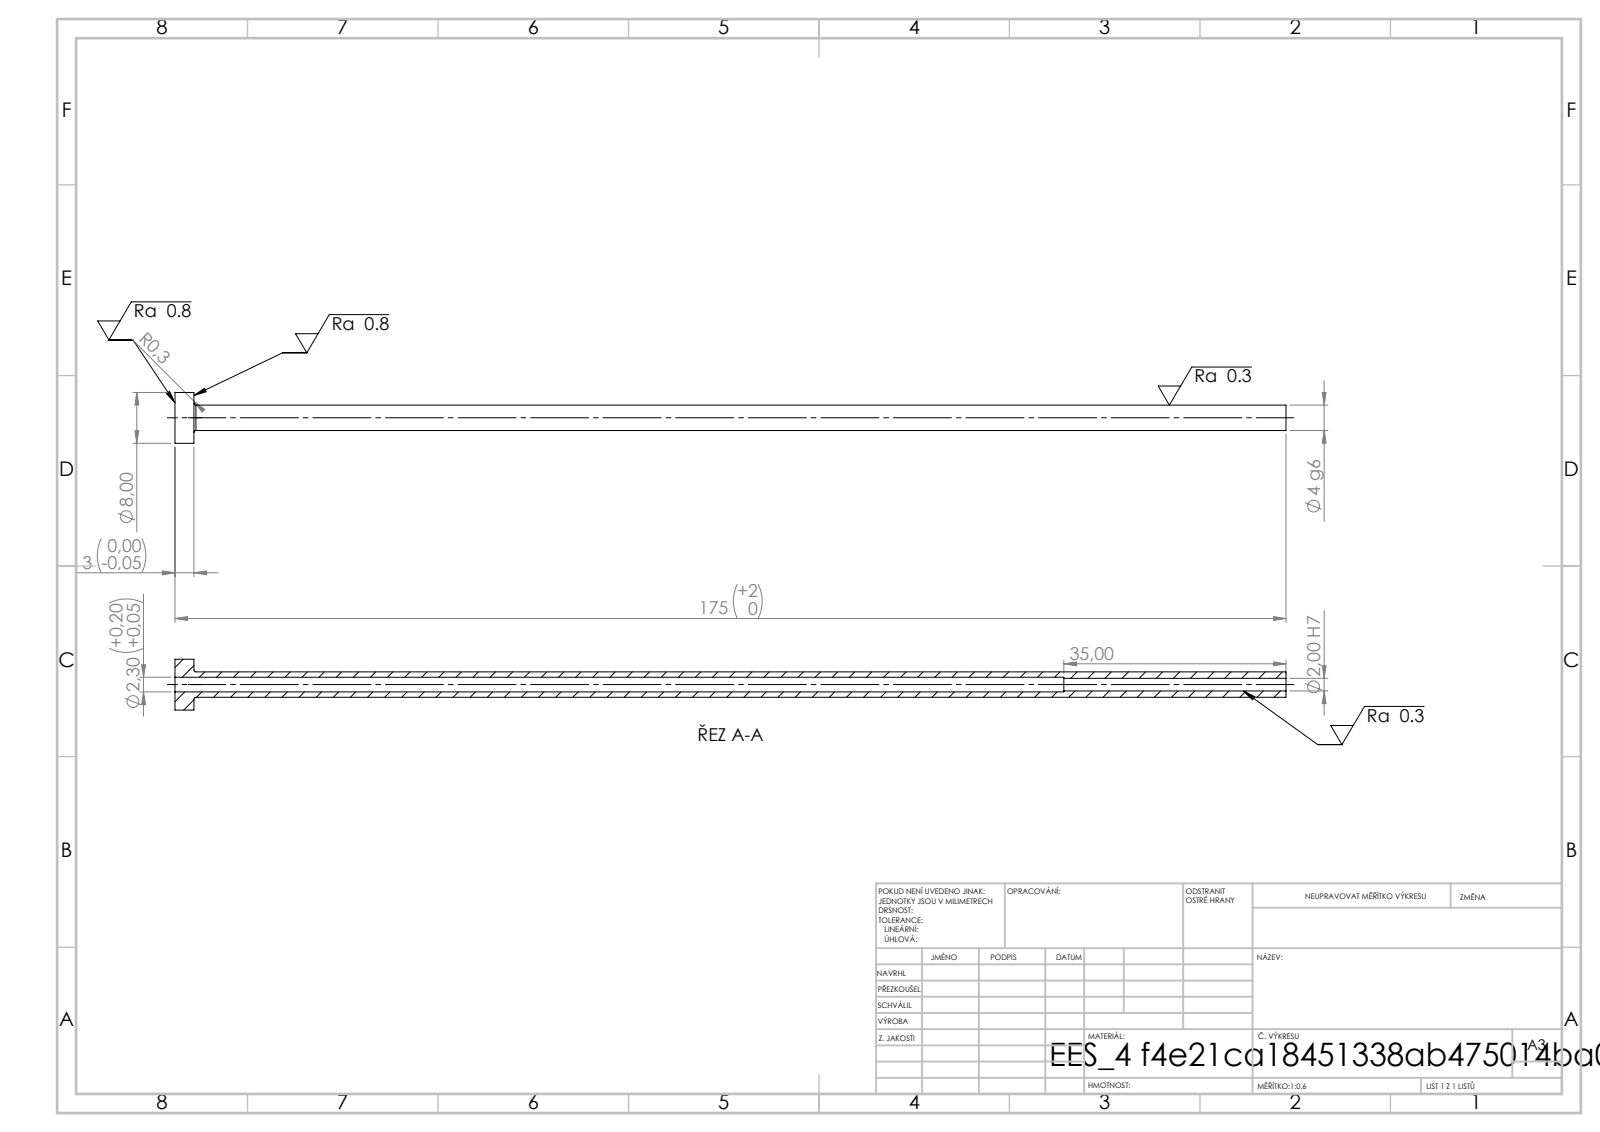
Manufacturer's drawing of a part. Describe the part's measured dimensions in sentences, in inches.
Its 3-D file was written by "SolidWorks 2019 (CONFIG_CONTROL_DESIGN)". It is 1 solid with 14 faces: 4 planar, 8 cylindrical and 2 other. Overall it measures 6.89 by 0.315 by 0.315 inches. Its volume is 0.099 cubic inches and its surface area 5.52 square inches. Round holes: 1 of diameter 0.079, 1 of diameter 0.091. Round bosses or shafts: 1 of diameter 0.315, 1 of diameter 0.157. The main face-to-face distances are 0.118, 6.89, 6.772, 5.512, 5.394, 1.378.
